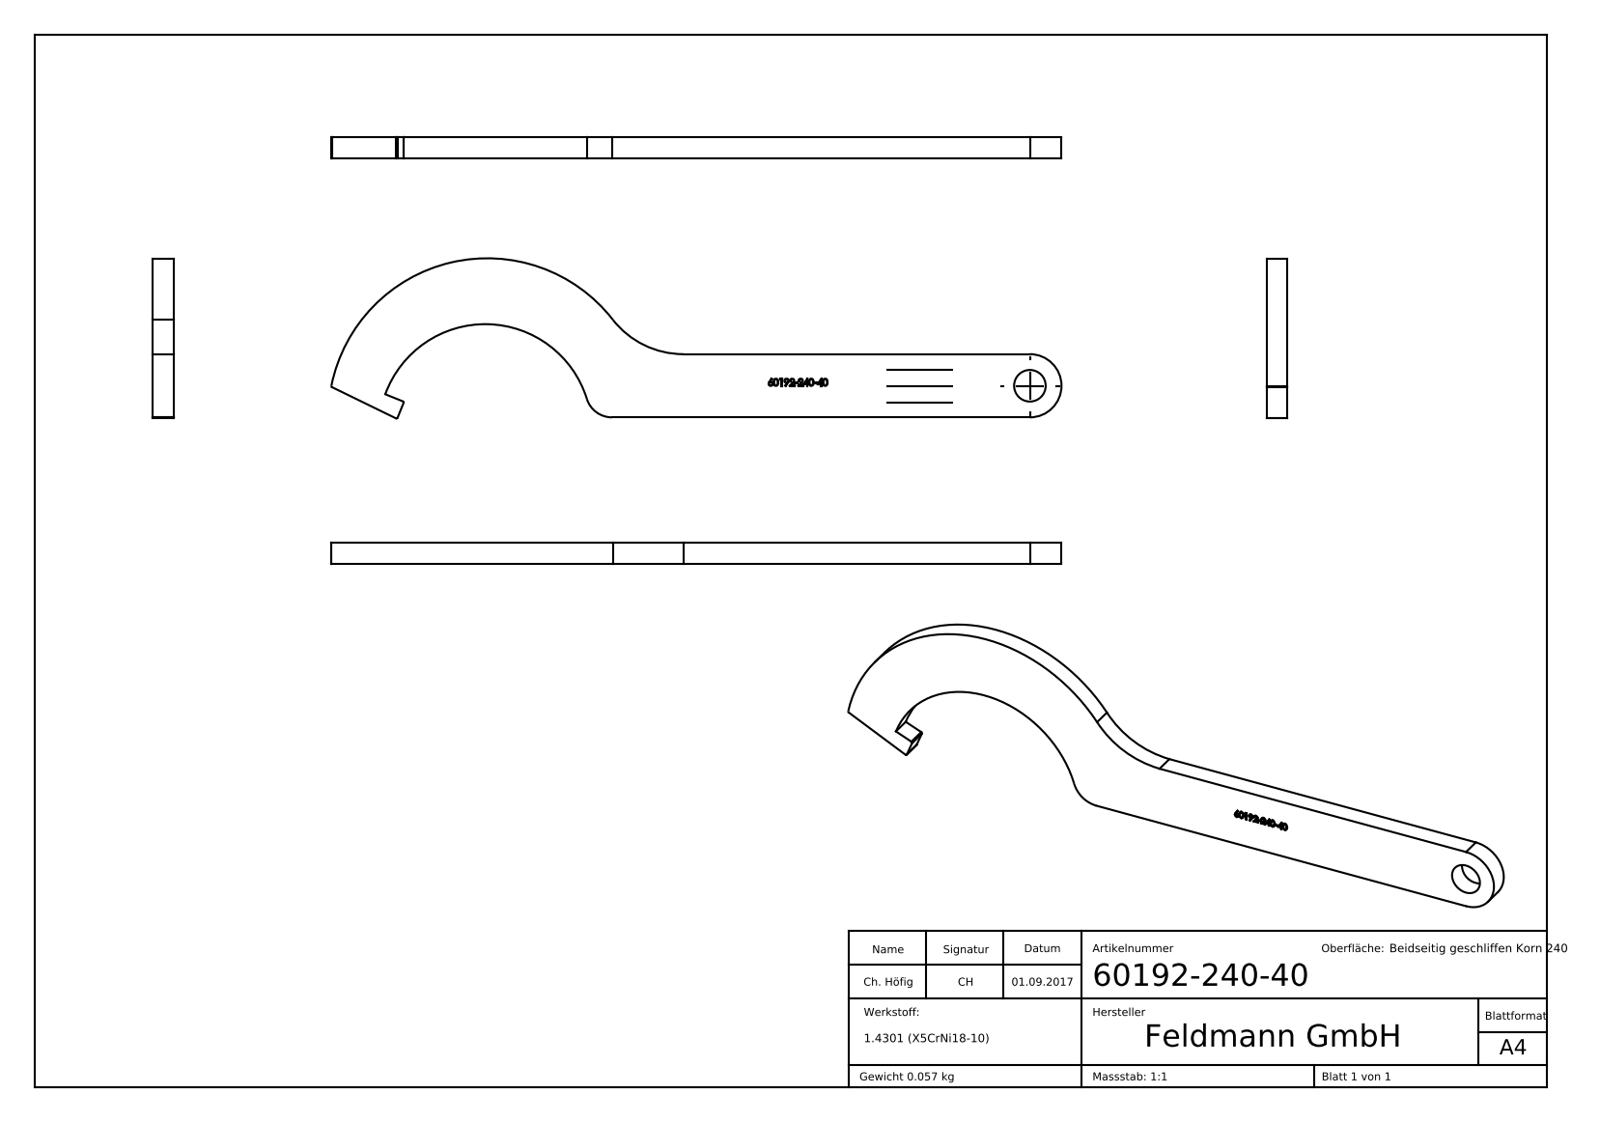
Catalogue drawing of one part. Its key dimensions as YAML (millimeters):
part_name: "60192-240-40"
step_written_by: "SolidWorks 2015 (CONFIG_CONTROL_DESIGN)"
units: millimeters
bodies: {solids: 1, faces: 152, planar: 84, cylindrical: 11, other: 57}
overall_size: [138.62, 30.4, 4]
volume: 7164
surface_area: 4993
round_holes:
  - {diameter: 6, count: 1}
partial_cylinders:
  - {radius: 0.25, count: 3}
  - {radius: 5, count: 1}
  - {radius: 6, count: 1}
  - {radius: 17, count: 1}
  - {radius: 20.2, count: 1}
  - {radius: 30.2, count: 1}
face_to_face_distances: [4, 12, 0.5, 3.5, 6, 0.31, 2.65, 4.9, 6.45, 0.45]
